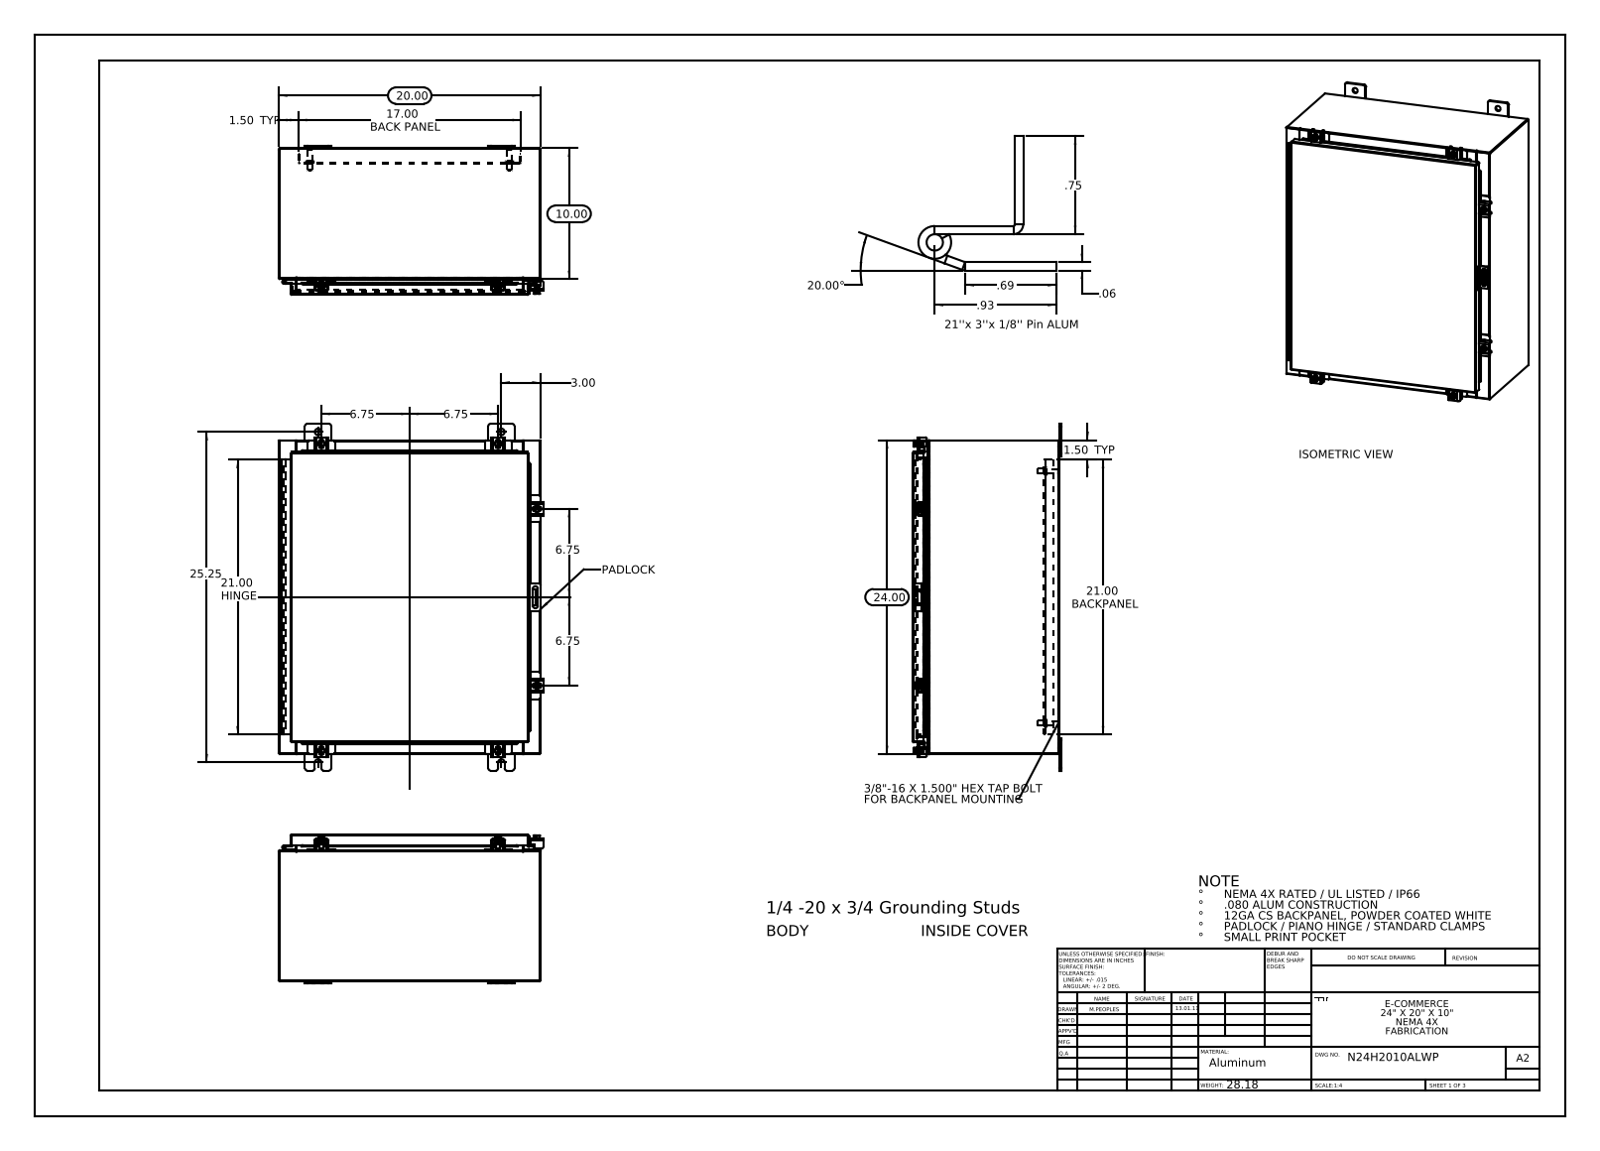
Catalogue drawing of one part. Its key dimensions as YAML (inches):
part_name: "N24H2010ALWP Mounting Studs; N24H2010ALWP Padlock Hasp; N24H2010ALWP Clamp Assembly; N24H2010ALWP (+8 more)"
step_written_by: "SolidWorks 2013 (CONFIG_CONTROL_DESIGN)"
units: inches
bodies: {solids: 49, faces: 1735, planar: 914, cylindrical: 713, other: 108}
overall_size: [26.5, 20.211, 11.389]
volume: 200.1
surface_area: 5064
round_holes:
  - {diameter: 0.5, count: 8}
  - {diameter: 0.213, count: 6}
  - {diameter: 0.26, count: 6}
  - {diameter: 0.125, count: 2}
  - {diameter: 0.125, count: 1}
round_bosses_or_shafts:
  - {diameter: 0.25, count: 7}
  - {diameter: 0.5, count: 6}
  - {diameter: 0.399, count: 6}
  - {diameter: 0.625, count: 4}
  - {diameter: 0.375, count: 4}
  - {diameter: 0.33, count: 4}
  - {diameter: 0.315, count: 2}
  - {diameter: 0.236, count: 2}
partial_cylinders:
  - {radius: 0.06, count: 30}
  - {radius: 0.013, count: 25}
  - {radius: 0.19, count: 24}
  - {radius: 0.088, count: 21}
  - {radius: 0.12, count: 12}
  - {radius: 0.141, count: 12}
  - {radius: 0.125, count: 10}
  - {radius: 0.05, count: 9}
face_to_face_distances: [0.075, 11.126, 19.925, 11.051, 11.201, 23.925, 0.104, 1, 1.075, 10.051]
hole_center_spacings: [21.369, 25.739, 13.5, 0.431, 0.934, 1.858, 2.275, 2.276]
